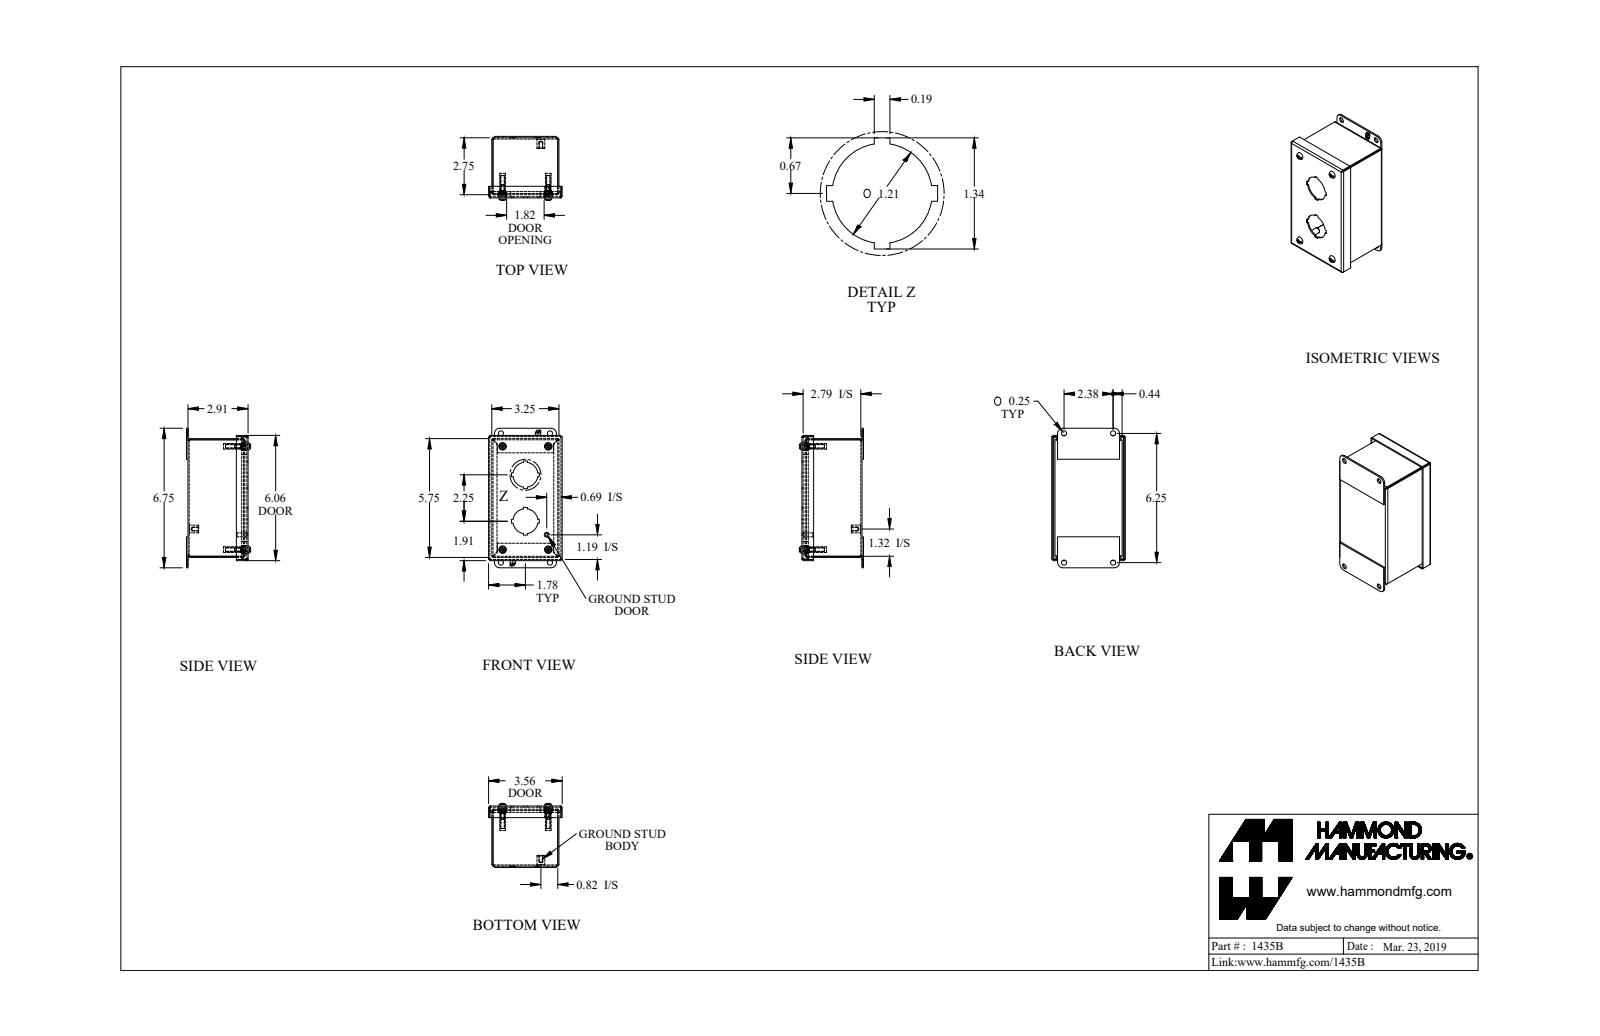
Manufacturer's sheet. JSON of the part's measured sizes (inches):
{"part_name": "1435B_Default", "step_written_by": "SolidWorks 2019 (CONFIG_CONTROL_DESIGN)", "units": "inches", "bodies": {"solids": 19, "faces": 587, "planar": 383, "cylindrical": 148, "other": 56}, "overall_size": [6.75, 3.562, 3.106], "volume_in3": 8.296, "surface_area_in2": 255.4, "round_holes": [[0.25, 8], [0.159, 4], [0.406, 4], [1.21, 2], [0.156, 1]], "round_bosses_or_shafts": [[0.39, 4], [0.19, 4], [0.148, 4], [0.275, 2], [0.275, 2], [0.375, 1], [0.25, 1], [0.188, 1]], "partial_cylinders_radius": [[0.029, 12], [0.086, 12], [0.16, 4], [0.171, 4], [0.25, 4]], "face_to_face_distances": [0.057, 2.85, 0.057, 3.193, 2.907, 2.793, 5.693, 3.136, 3.25, 0.156], "hole_center_spacings": [5, 2.376, 0.63, 0.631, 1.765, 2.21, 2.211, 2.377]}
